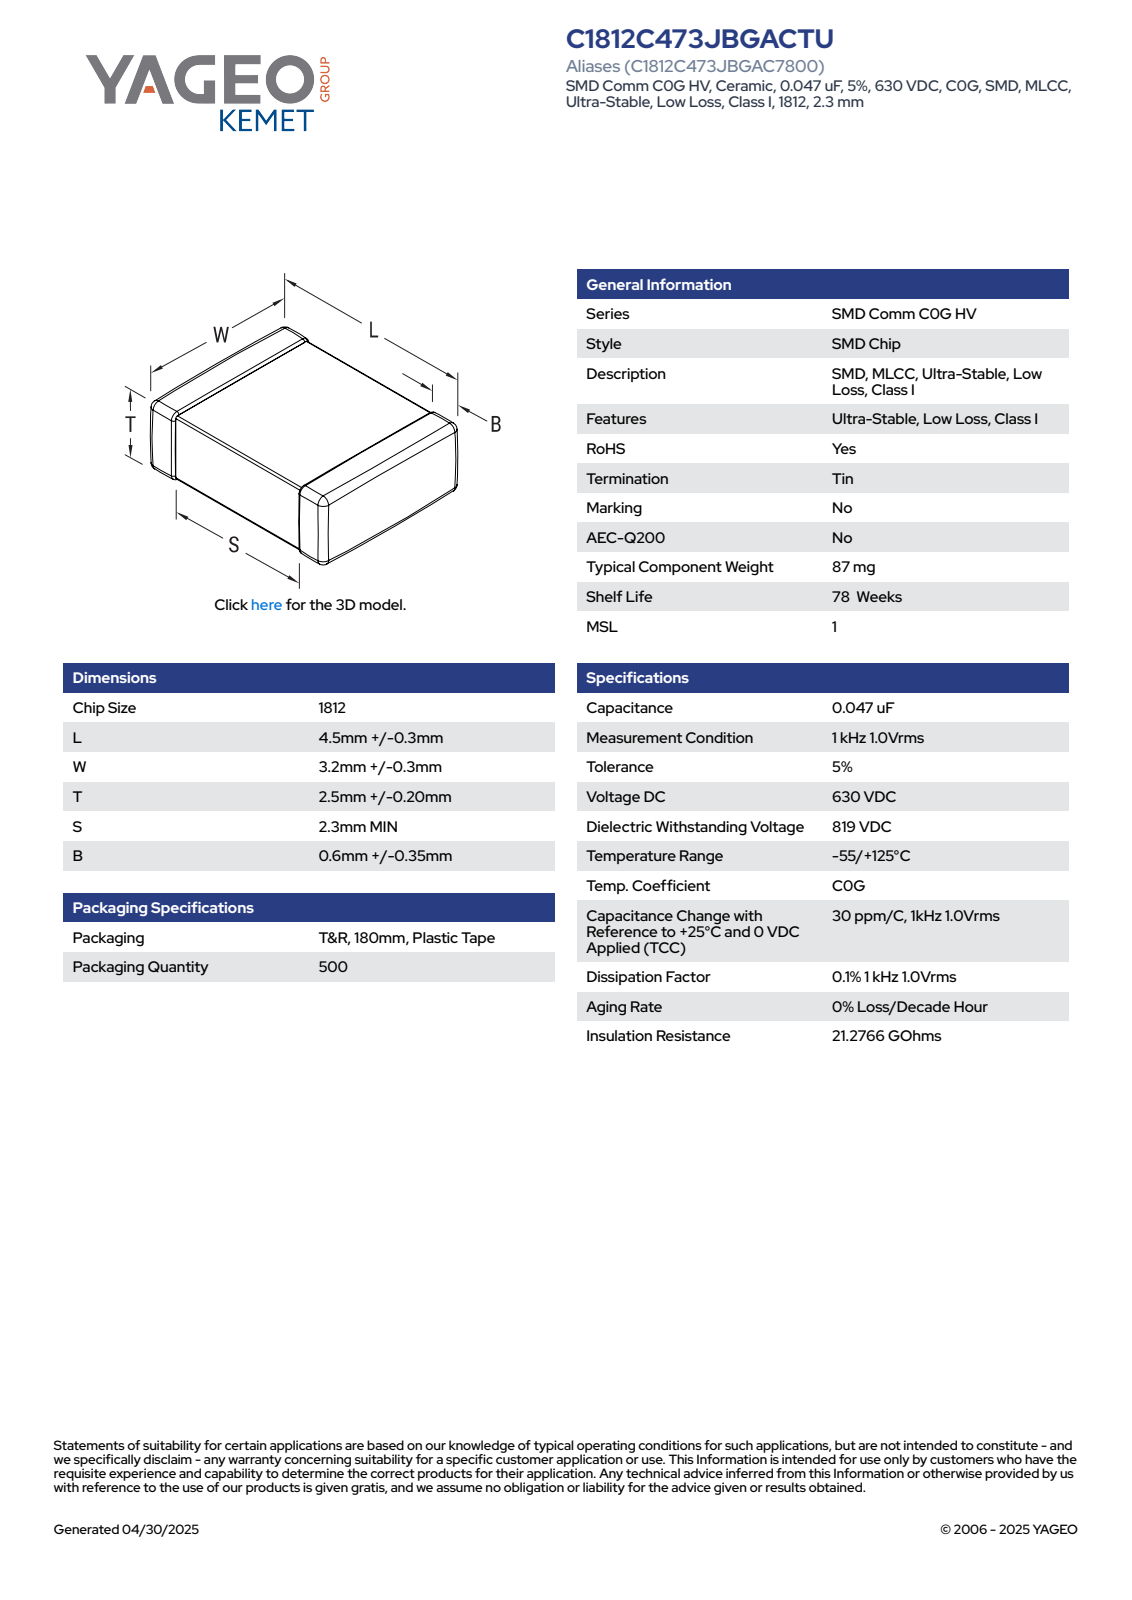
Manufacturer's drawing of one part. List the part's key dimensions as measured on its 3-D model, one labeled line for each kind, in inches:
Part name (STEP PRODUCT): CCS_CCSTD_1812_L4.8W3.5T2.7B0.6
STEP written by: SolidWorks 2021 (AUTOMOTIVE_DESIGN)
Units: inches
Bodies: 4 solids, 125 faces (71 planar, 38 cylindrical, 16 other)
Overall size (bounding box): 0.189 × 0.138 × 0.106
Volume: 0.003 in³ · Surface area: 0.12 in²
Main face-to-face distances: 0.104, 0.101, 0.189, 0.135, 0.132, 0.106, 0.138, 0.082, 0.107, 0.102
